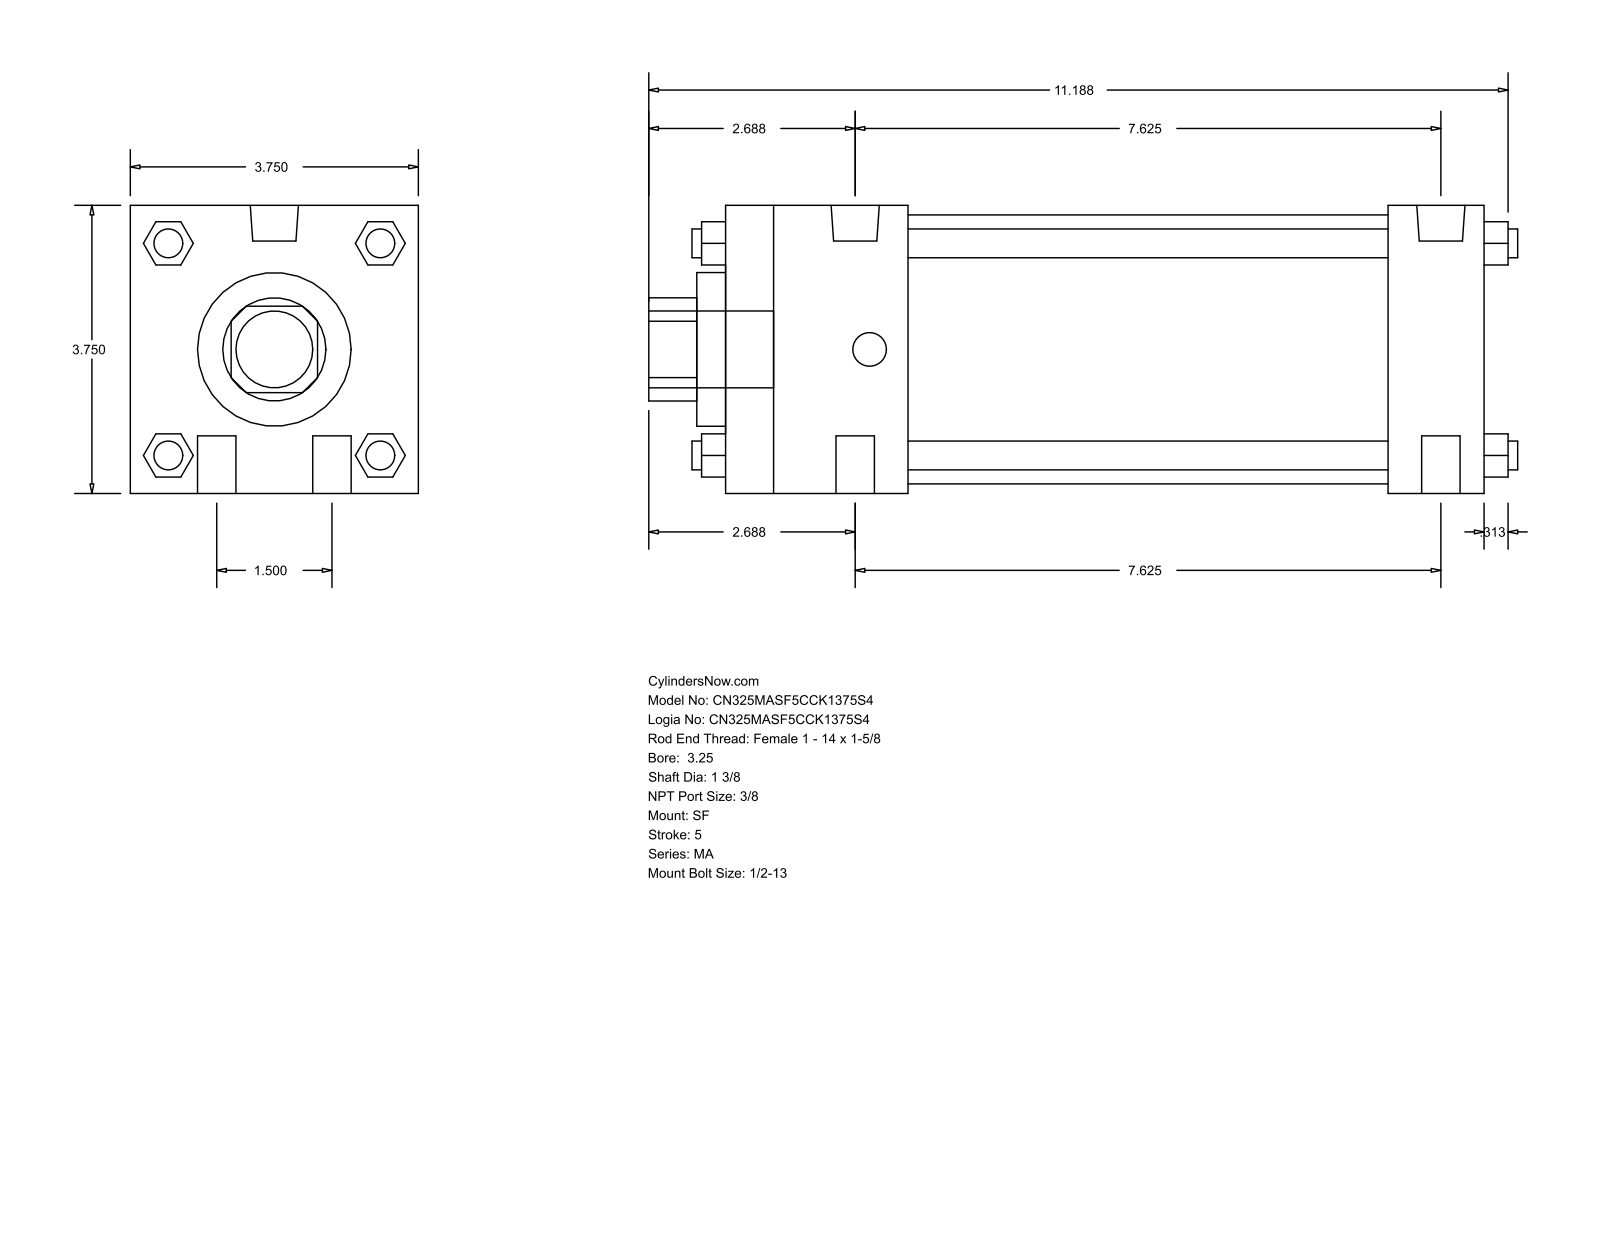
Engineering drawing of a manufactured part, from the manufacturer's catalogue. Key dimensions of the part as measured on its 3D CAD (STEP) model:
Part name (STEP PRODUCT): MA_SF__0325_1.375
STEP written by: GSSL Pune (CONFIG_CONTROL_DESIGN)
Units: millimetres
Bodies: 0 solids, 124 faces (94 planar, 30 cylindrical, 0 other)
Overall size (bounding box): 287.34 × 95.25 × 95.25
Round holes (diameter × count): ⌀34.92 ×1, ⌀50.8 ×1, ⌀88.9 ×1
Round bosses / shafts (diameter × count): ⌀12.7 ×4, ⌀9.53 ×4, ⌀15.93 ×2, ⌀11.11 ×2, ⌀25.4 ×1
Partial cylindrical surfaces — rounded edges, fillets, slot ends (radius × count): R17.06 ×1
Main face-to-face distances: 95.24, 250.83, 219.07, 31.76, 60.32, 158.75, 190.51, 9.52, 69.84, 228.59
